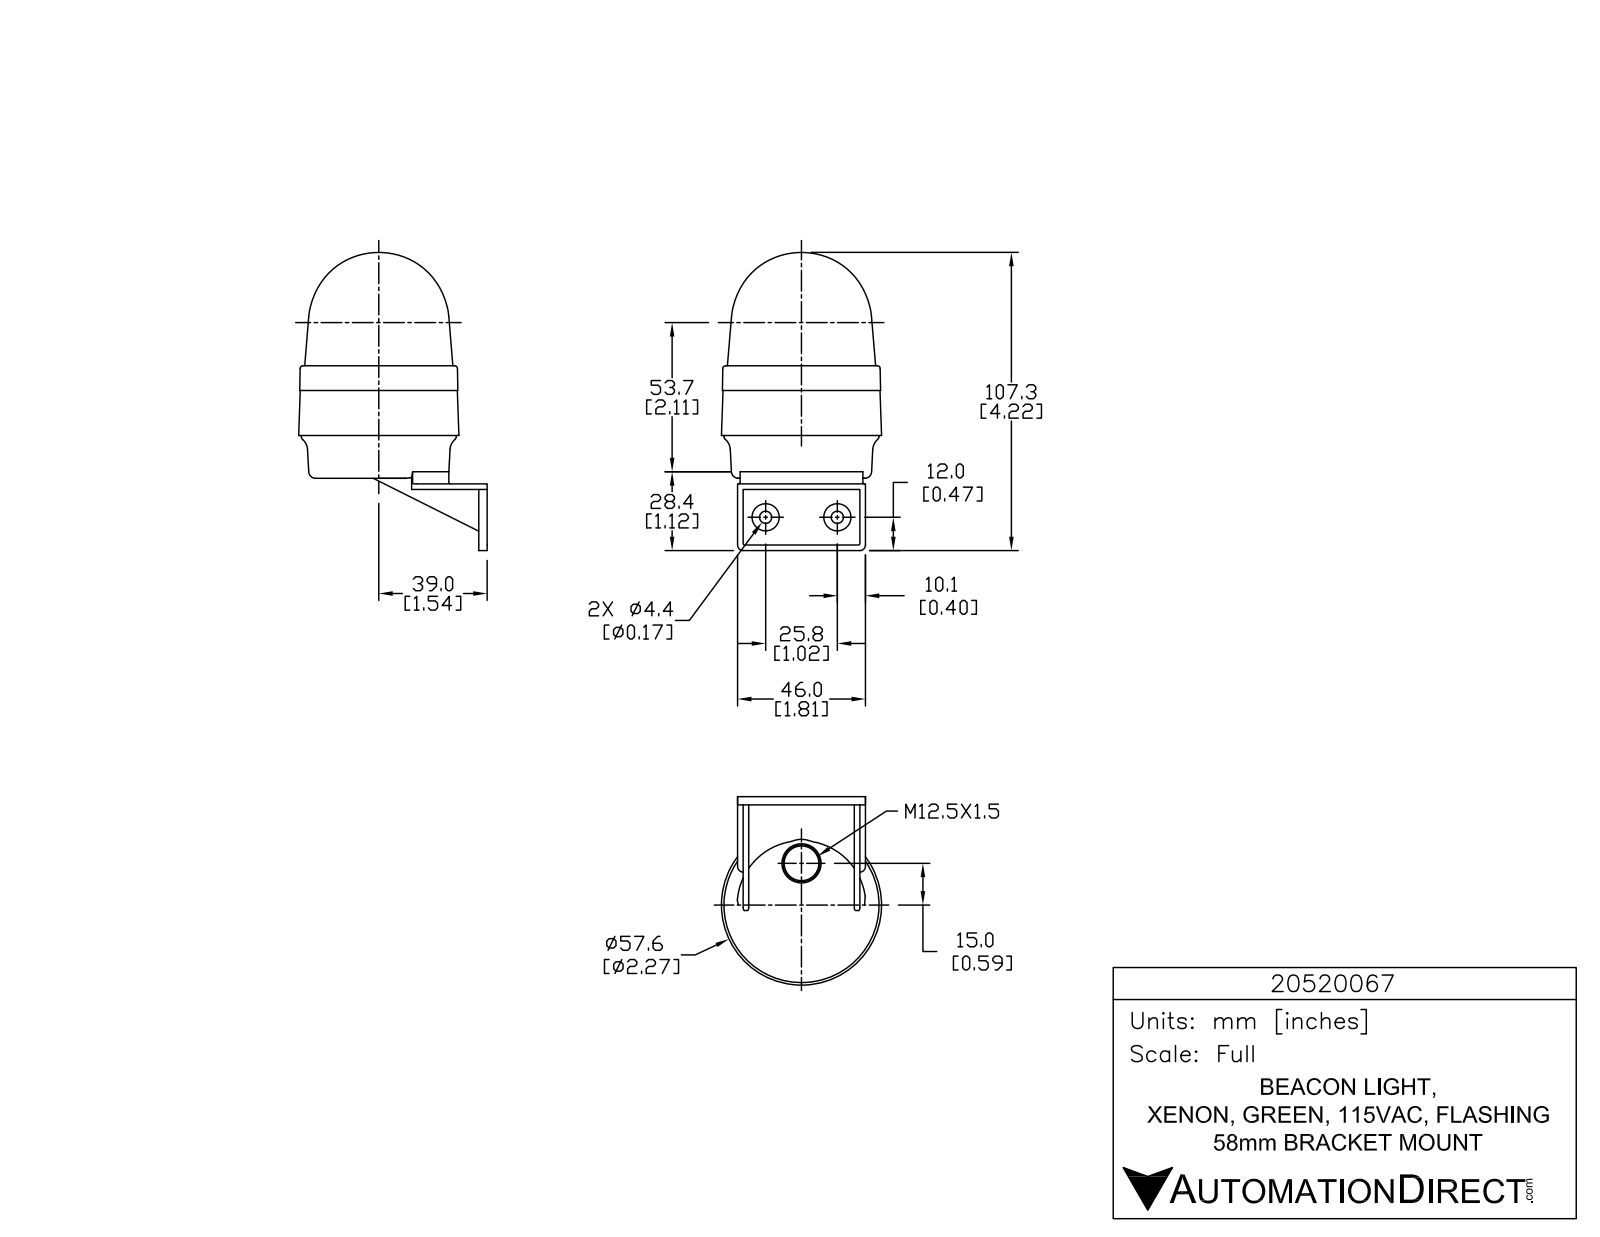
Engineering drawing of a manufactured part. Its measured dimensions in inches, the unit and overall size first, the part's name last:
Units: inches
Overall size (bounding box): 4.225 × 2.852 × 2.407
Round holes (diameter × count): ⌀0.039 ×3, ⌀0.173 ×2
Round bosses / shafts (diameter × count): ⌀0.226 ×3, ⌀0.056 ×3, ⌀0.386 ×2, ⌀2.197 ×1
Partial cylindrical surfaces — rounded edges, fillets, slot ends (radius × count): R0.008 ×6, R0.008 ×6, R0.008 ×6, R0.02 ×6, R0.131 ×6, R0.079 ×4, R0.004 ×3, R0.005 ×3
Main face-to-face distances: 0.079, 0.157, 1.575, 1.654, 0.039, 0.118, 1.496, 0.866, 0.945, 0.764
Hole centre spacings: 1.016
Volume: 10.27 in³ · Surface area: 33.38 in²
Bodies: 1 solid, 828 faces (551 planar, 179 cylindrical, 98 other)
Part name (STEP PRODUCT): 20520067
STEP written by: SolidWorks 2015 (AUTOMOTIVE_DESIGN)
